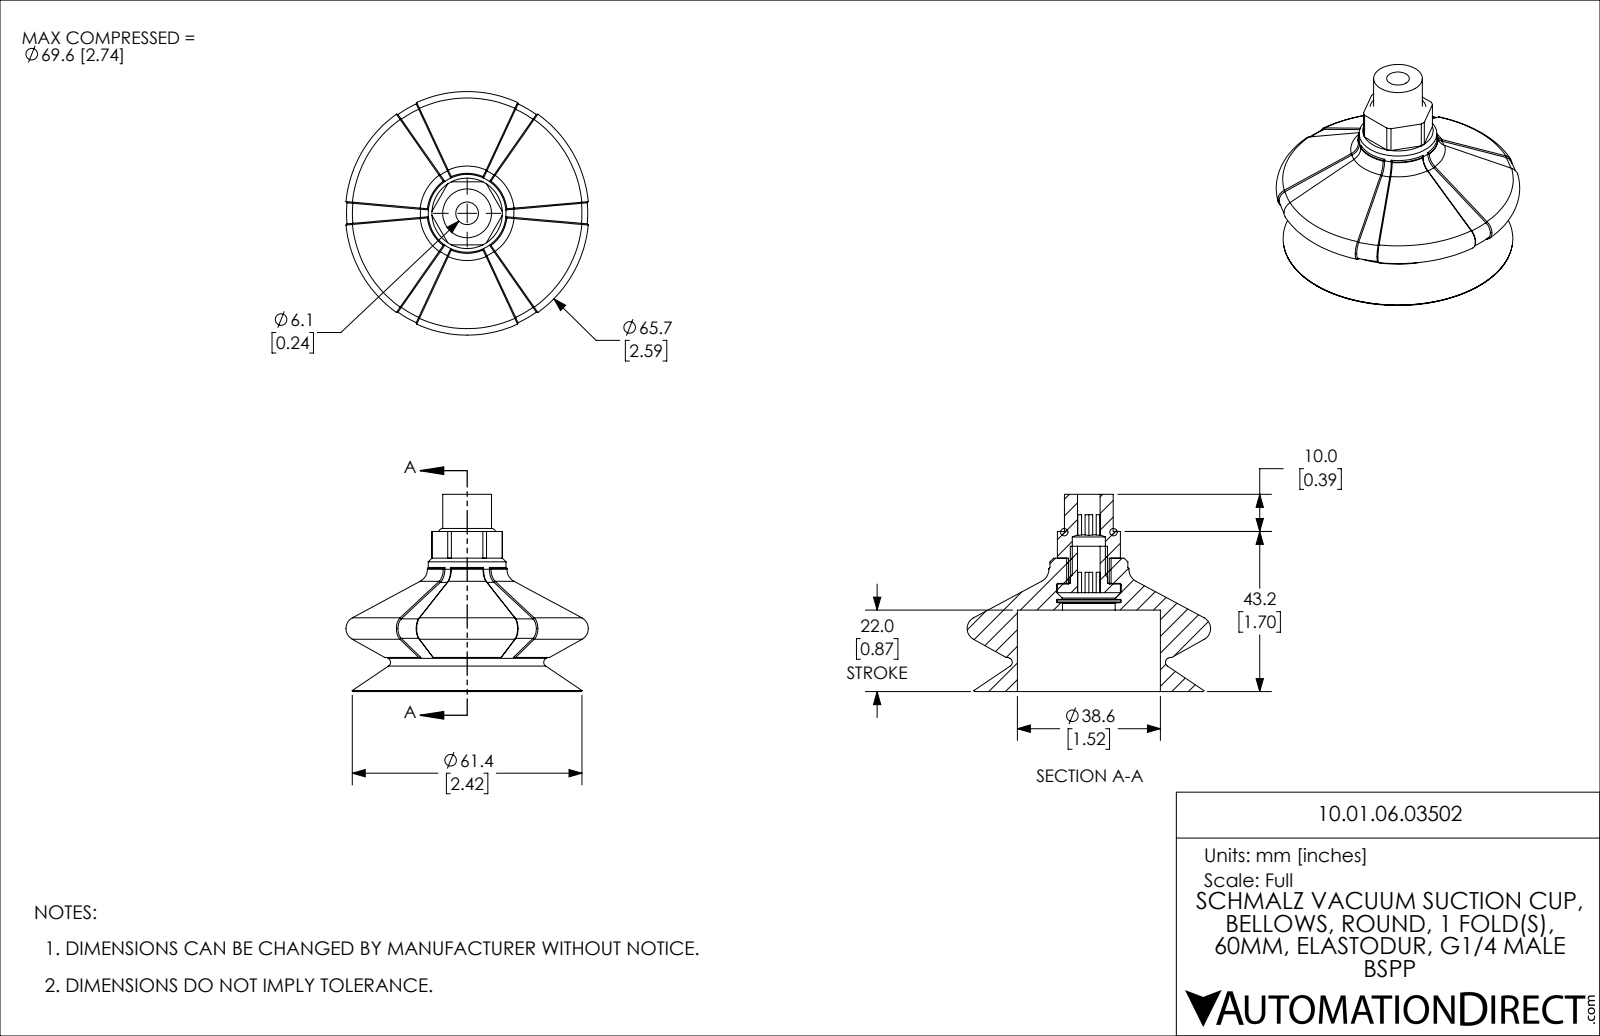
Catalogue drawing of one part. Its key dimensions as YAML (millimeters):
part_name: "10.01.06.03502"
step_written_by: "SolidWorks 2021 (CONFIG_CONTROL_DESIGN)"
units: millimeters
bodies: {solids: 4, faces: 259, planar: 72, cylindrical: 41, other: 146}
overall_size: [65.7, 65.39, 53.2]
volume: 42252
surface_area: 19059
round_holes:
  - {diameter: 6.1, count: 1}
  - {diameter: 8.92, count: 1}
  - {diameter: 10.2, count: 1}
  - {diameter: 11, count: 1}
  - {diameter: 14.22, count: 1}
  - {diameter: 17.3, count: 1}
  - {diameter: 17.5, count: 1}
  - {diameter: 38.6, count: 1}
round_bosses_or_shafts:
  - {diameter: 21, count: 1}
  - {diameter: 17, count: 1}
  - {diameter: 13.16, count: 1}
  - {diameter: 12, count: 1}
  - {diameter: 10, count: 1}
partial_cylinders:
  - {radius: 9.5, count: 1}
  - {radius: 10.8, count: 1}
face_to_face_distances: [22, 14, 36, 7.2, 7, 26.7, 4.7, 9.3, 17, 29.2]
